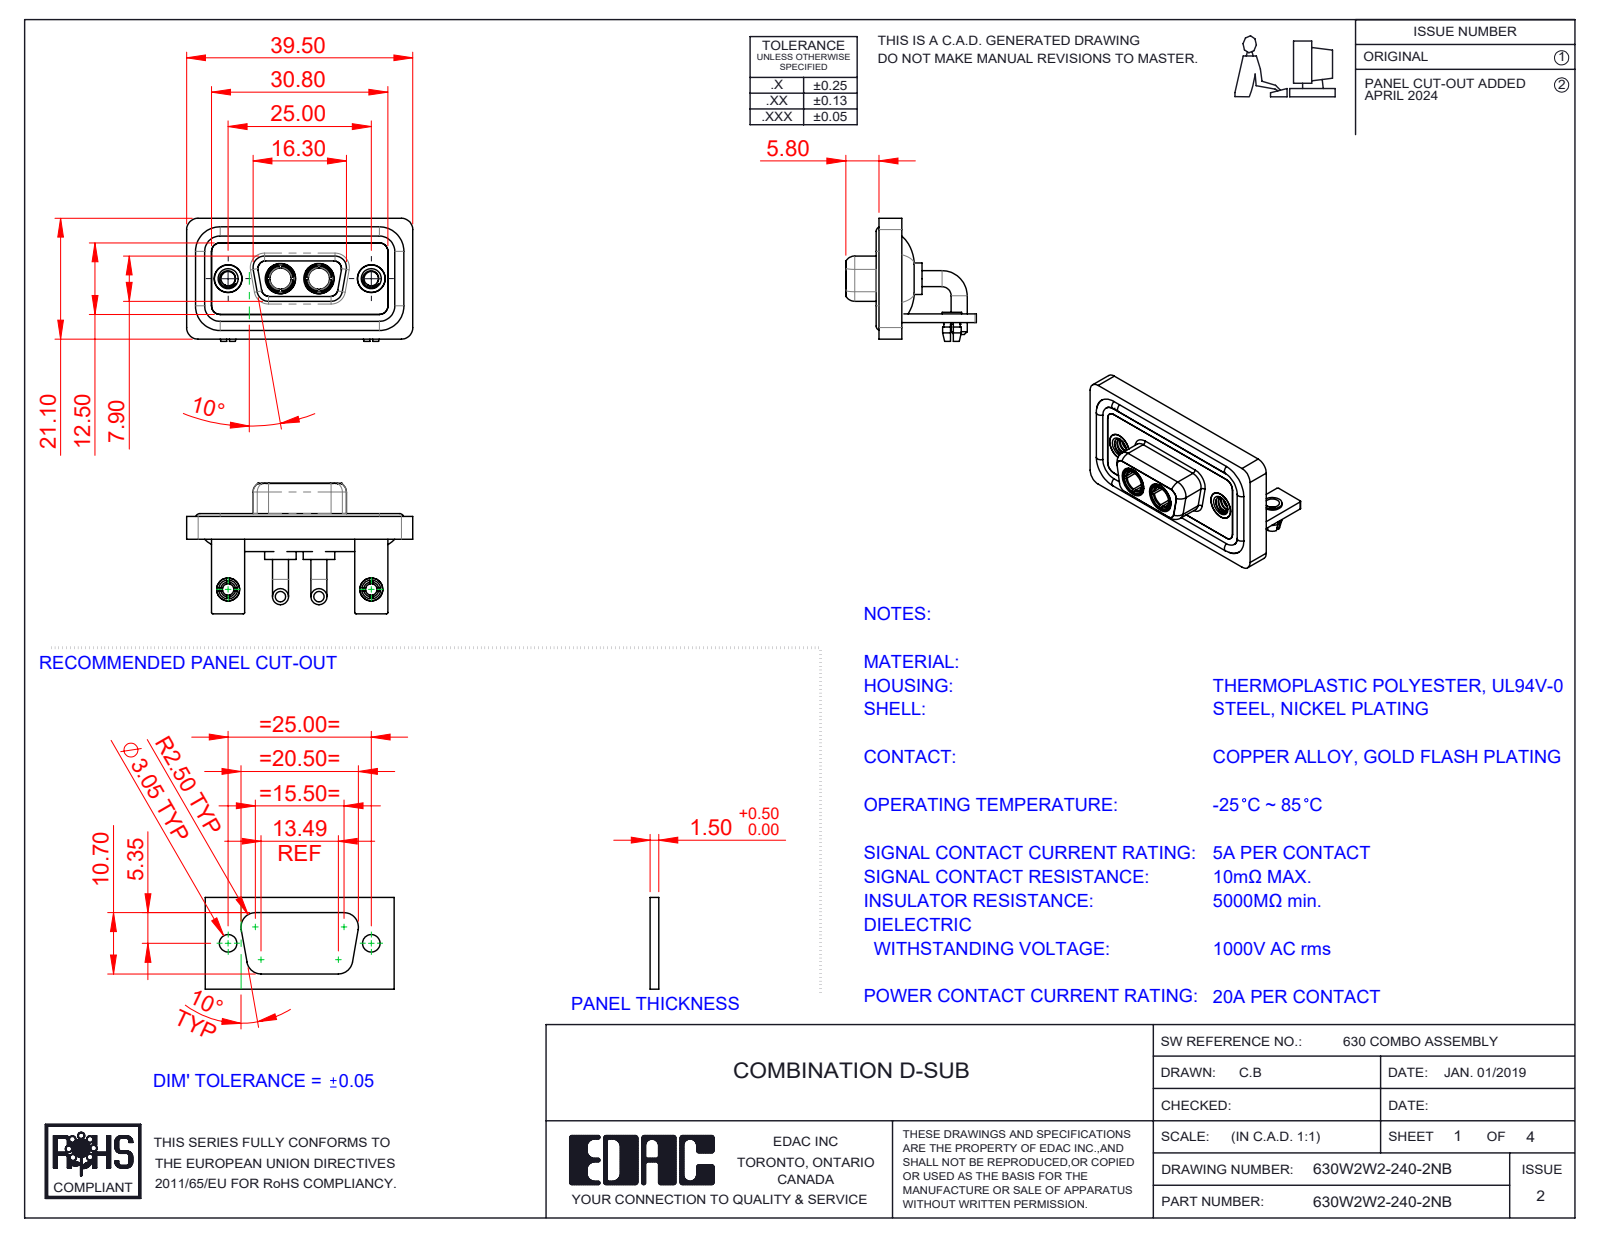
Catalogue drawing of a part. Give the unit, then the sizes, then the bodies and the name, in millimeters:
Units: millimetres
Overall size (bounding box): 39.5 × 22.8 × 21.5
Round holes (diameter × count): ⌀2.5 ×4, ⌀4.85 ×4, ⌀2 ×2, ⌀3.2 ×2, ⌀3.7 ×2, ⌀4 ×2, ⌀4.05 ×2, ⌀5 ×2, ⌀5.3 ×2
Round bosses / shafts (diameter × count): ⌀2.8 ×4, ⌀1.6 ×4, ⌀5.5 ×2, ⌀5.2 ×2, ⌀4.96 ×2, ⌀4.95 ×2, ⌀4.8 ×2, ⌀4.75 ×2
Partial cylindrical surfaces — rounded edges, fillets, slot ends (radius × count): R2 ×19, R1.5 ×18, R0.25 ×16, R1.35 ×8, R1.6 ×8, R0.5 ×5, R0.6 ×4, R0.65 ×4
Main face-to-face distances: 0.4, 2.9, 1.5, 1.8, 1.1, 3.7, 0.8, 2.5, 1.6, 3.1
Hole centre spacings: 9.14, 15.86, 25, 6.72
Volume: 5 211 mm³ · Surface area: 8 735 mm²
Bodies: 15 solids, 676 faces (231 planar, 292 cylindrical, 153 other)
Part name (STEP PRODUCT): 630Combo Housing_2W2; Power Socket_20A RA; 630Combo Board Lock_50 Contacts; 630Combo Shell Front_09 Contacts (+5 more)
STEP written by: SolidWorks 2023 (CONFIG_CONTROL_DESIGN)
